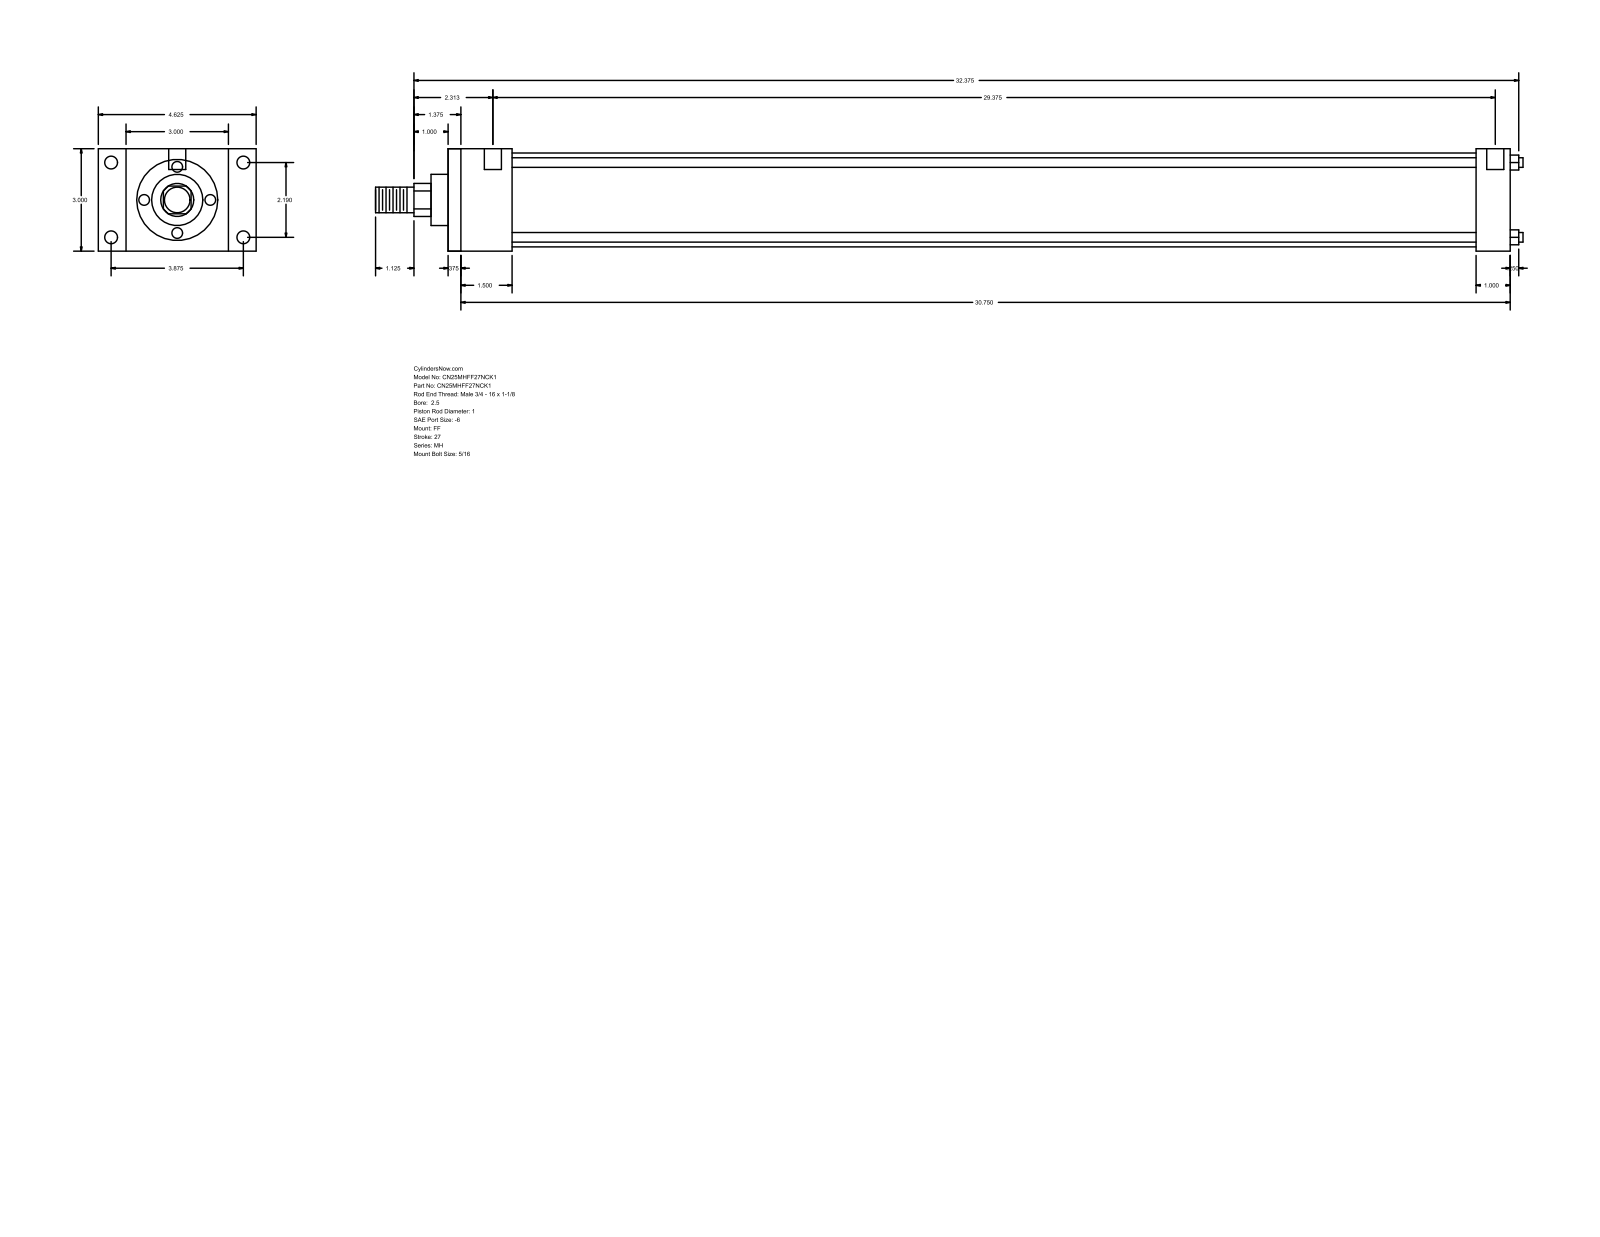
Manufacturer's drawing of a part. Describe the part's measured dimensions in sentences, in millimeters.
The part is named "MH_FF__0250_1". Its 3-D file was written by "GSSL Pune (CONFIG_CONTROL_DESIGN)". It is 0 solids with 92 faces: 64 planar, 28 cylindrical and 0 other. Overall it measures 854.08 by 117.47 by 76.2 millimeters. Round holes: 4 of diameter 5.56, 4 of diameter 9.53, 2 of diameter 12.7. Round bosses or shafts: 4 of diameter 7.14, 1 of diameter 69.85, 1 of diameter 38.1, 1 of diameter 25.4, 1 of diameter 19.05. Partial cylindrical surfaces (rounded edges, fillets, slot ends): 1 of radius 12.29. The main face-to-face distances are 76.2, 790.58, 9.52, 781.06, 25.4, 47.63, 765.18, 38.11, 755.66, 717.55. The hole center spacings are 55.62, 98.42, 113.05, 754.06, 3.18, 4.76, 746.12, 749.3.
